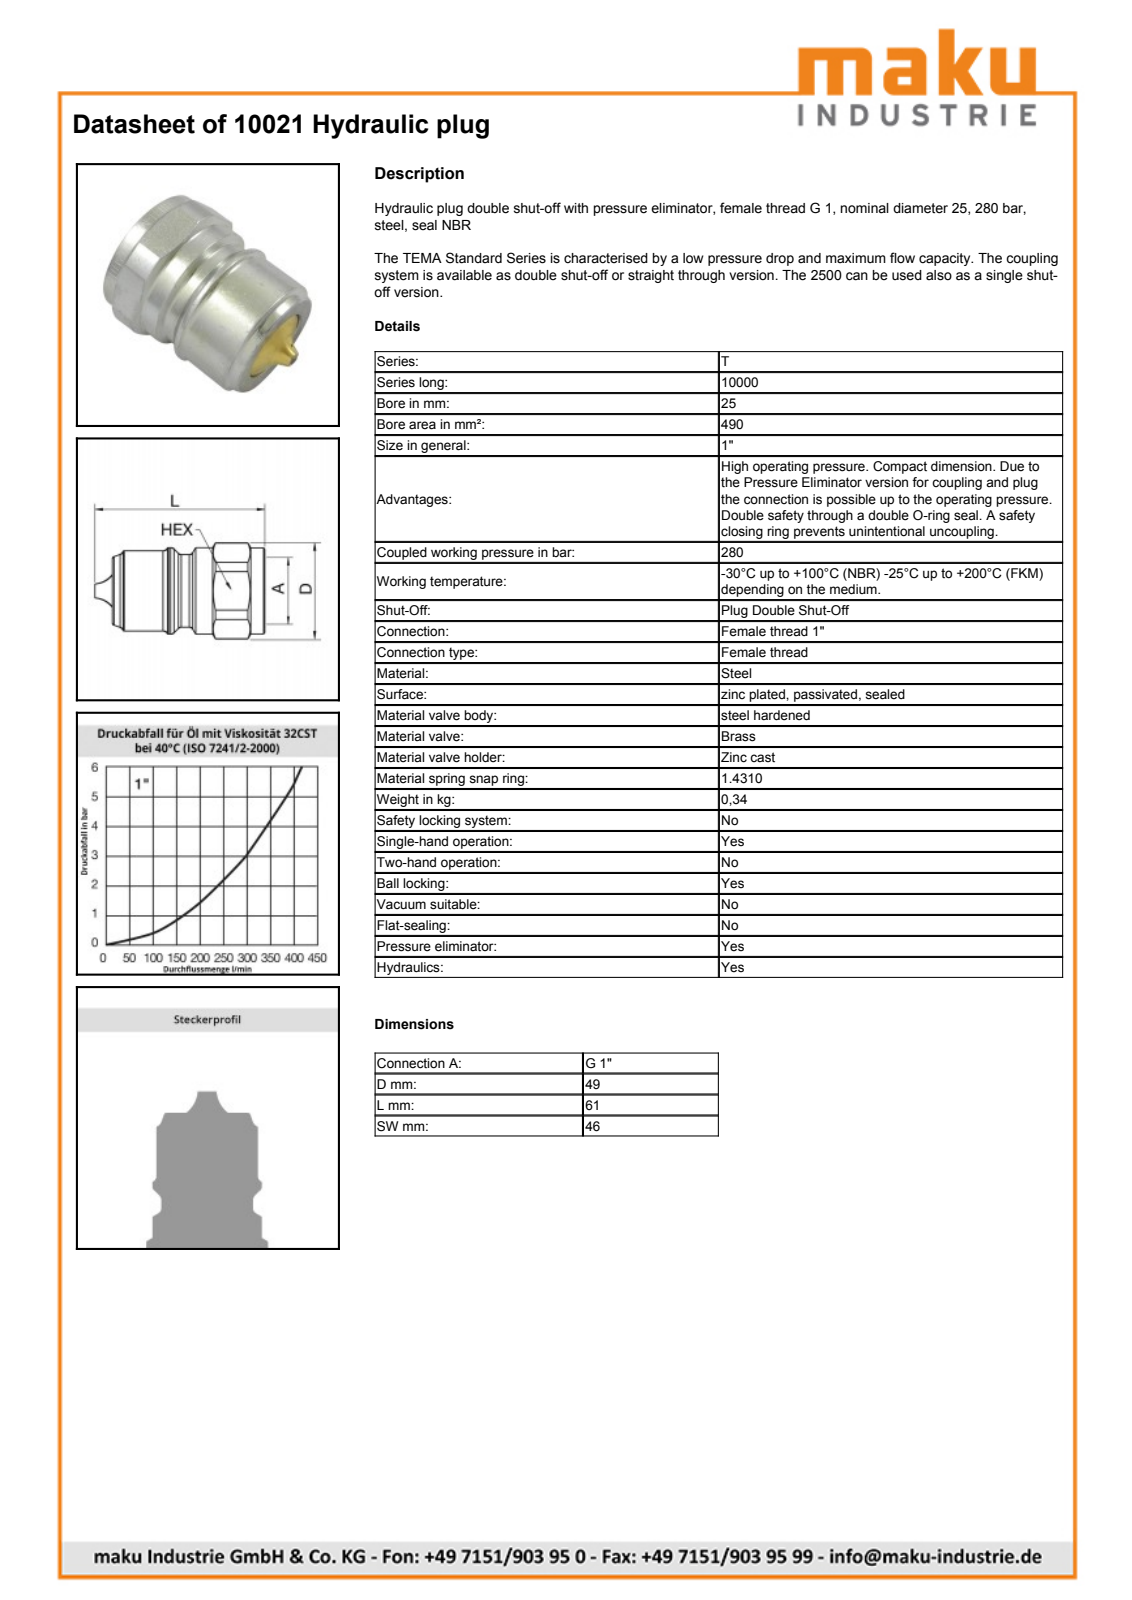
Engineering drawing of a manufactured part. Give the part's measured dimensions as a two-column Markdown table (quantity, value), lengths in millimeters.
| quantity | value |
| --- | --- |
| part name | 10021 |
| STEP written by | SolidWorks 2009 (AUTOMOTIVE_DESIGN) |
| units | millimeters |
| bodies | 1 solid, 79 faces (13 planar, 24 cylindrical, 42 other) |
| overall size | 61.6 × 49 × 46 |
| volume | 62 404 mm³ |
| surface area | 12 920 mm² |
| round holes (diameter × count) | 2.85 × 1, 3.93 × 1, 24.4 × 1, 30.29 × 1 |
| round bosses / shafts (diameter × count) | 44 × 1, 43.55 × 1, 41.2 × 1, 38.1 × 1 |
| partial cylindrical surfaces (radius × count) | 24.5 × 1 |
| main face-to-face distances | 22, 32, 54, 46, 7.15, 39.15, 61.15, 7.2, 39.2, 61.2 |
